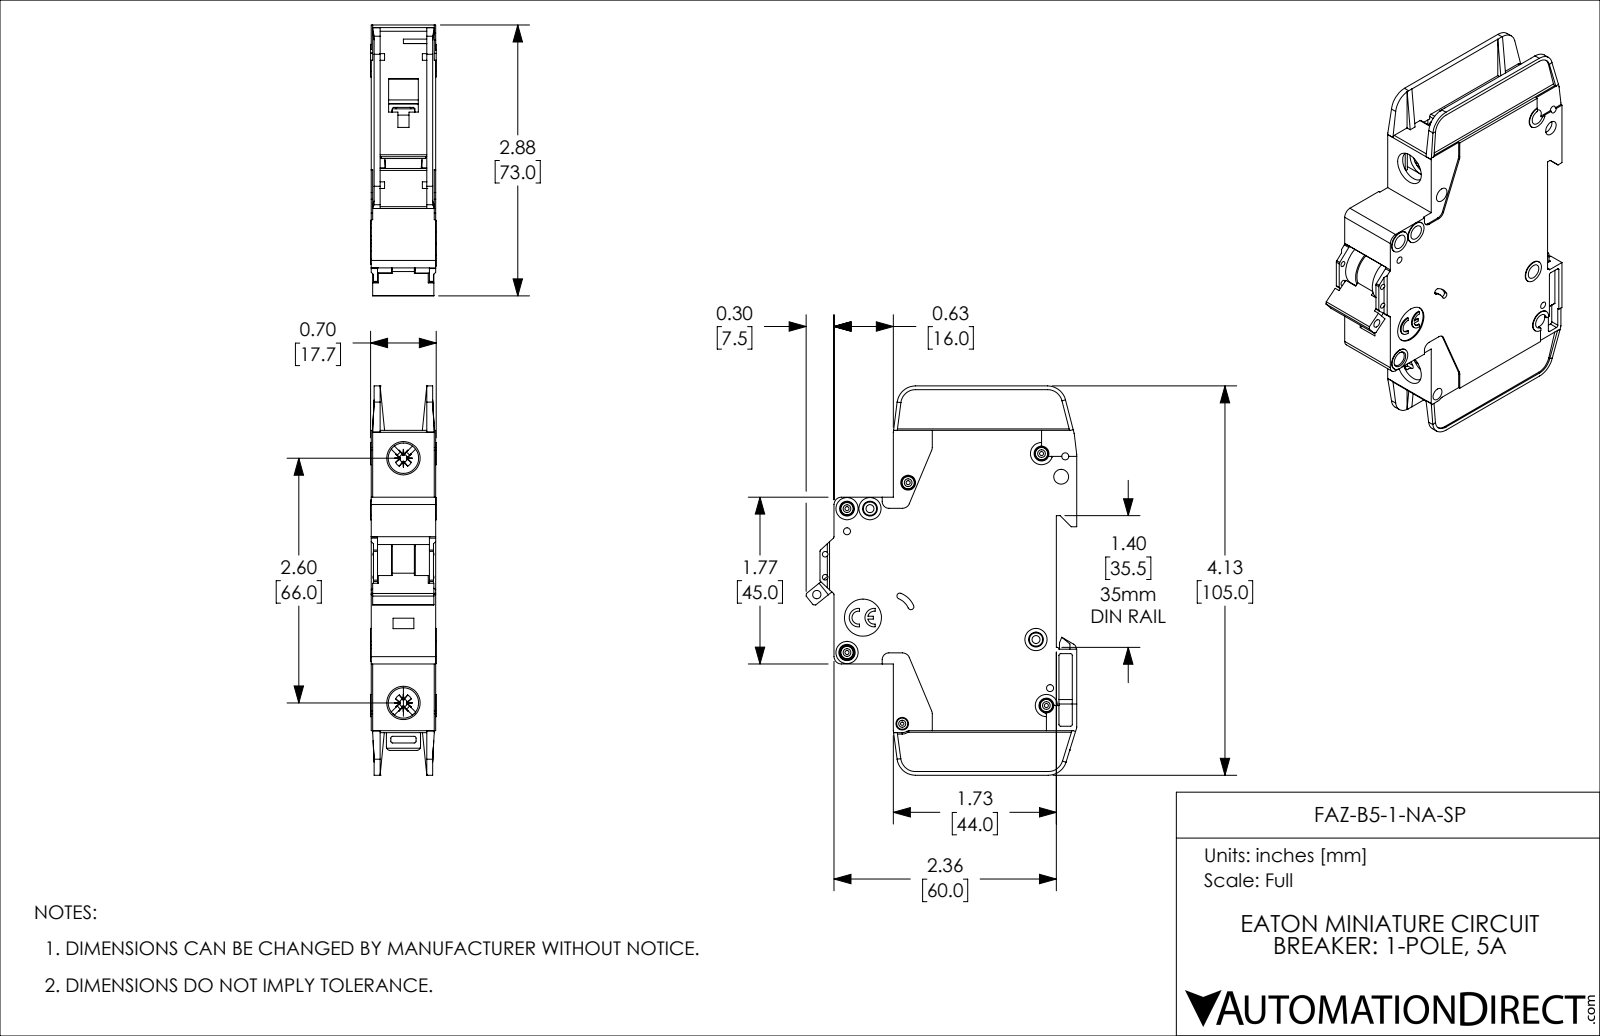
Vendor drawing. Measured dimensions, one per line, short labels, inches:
name: FAZ-B5-1-NA-SP
written by: SolidWorks 2019 (AUTOMOTIVE_DESIGN)
unit: in
bodies: 1 solid, 1127 faces (671 planar, 357 cylindrical, 99 other)
size: 4.134 × 2.876 × 0.697
volume: 4.682 in³; area: 41.01 in²
holes: 8× ⌀0.157, 5× ⌀0.043, 4× ⌀0.075, 2× ⌀0.059, 2× ⌀0.085, 2× ⌀0.323, 1× ⌀0.035, 1× ⌀0.089, 1× ⌀0.098, 1× ⌀0.134, 1× ⌀0.394
bosses: 5× ⌀0.13, 4× ⌀0.236, 2× ⌀0.118, 1× ⌀0.098
rounds: 42× R0.02, 10× R0.016, 10× R0.039, 8× R0.079, 5× R0.197, 4× R0.008, 4× R0.026, 4× R0.043
face distances: 0.047, 0.685, 0.591, 0.638, 0.094, 0.543, 0.016, 0.031, 0.496, 0.575
hole spacings: 0.244, 0.537, 0.87, 0.189, 0.199, 0.204, 0.221, 0.24
